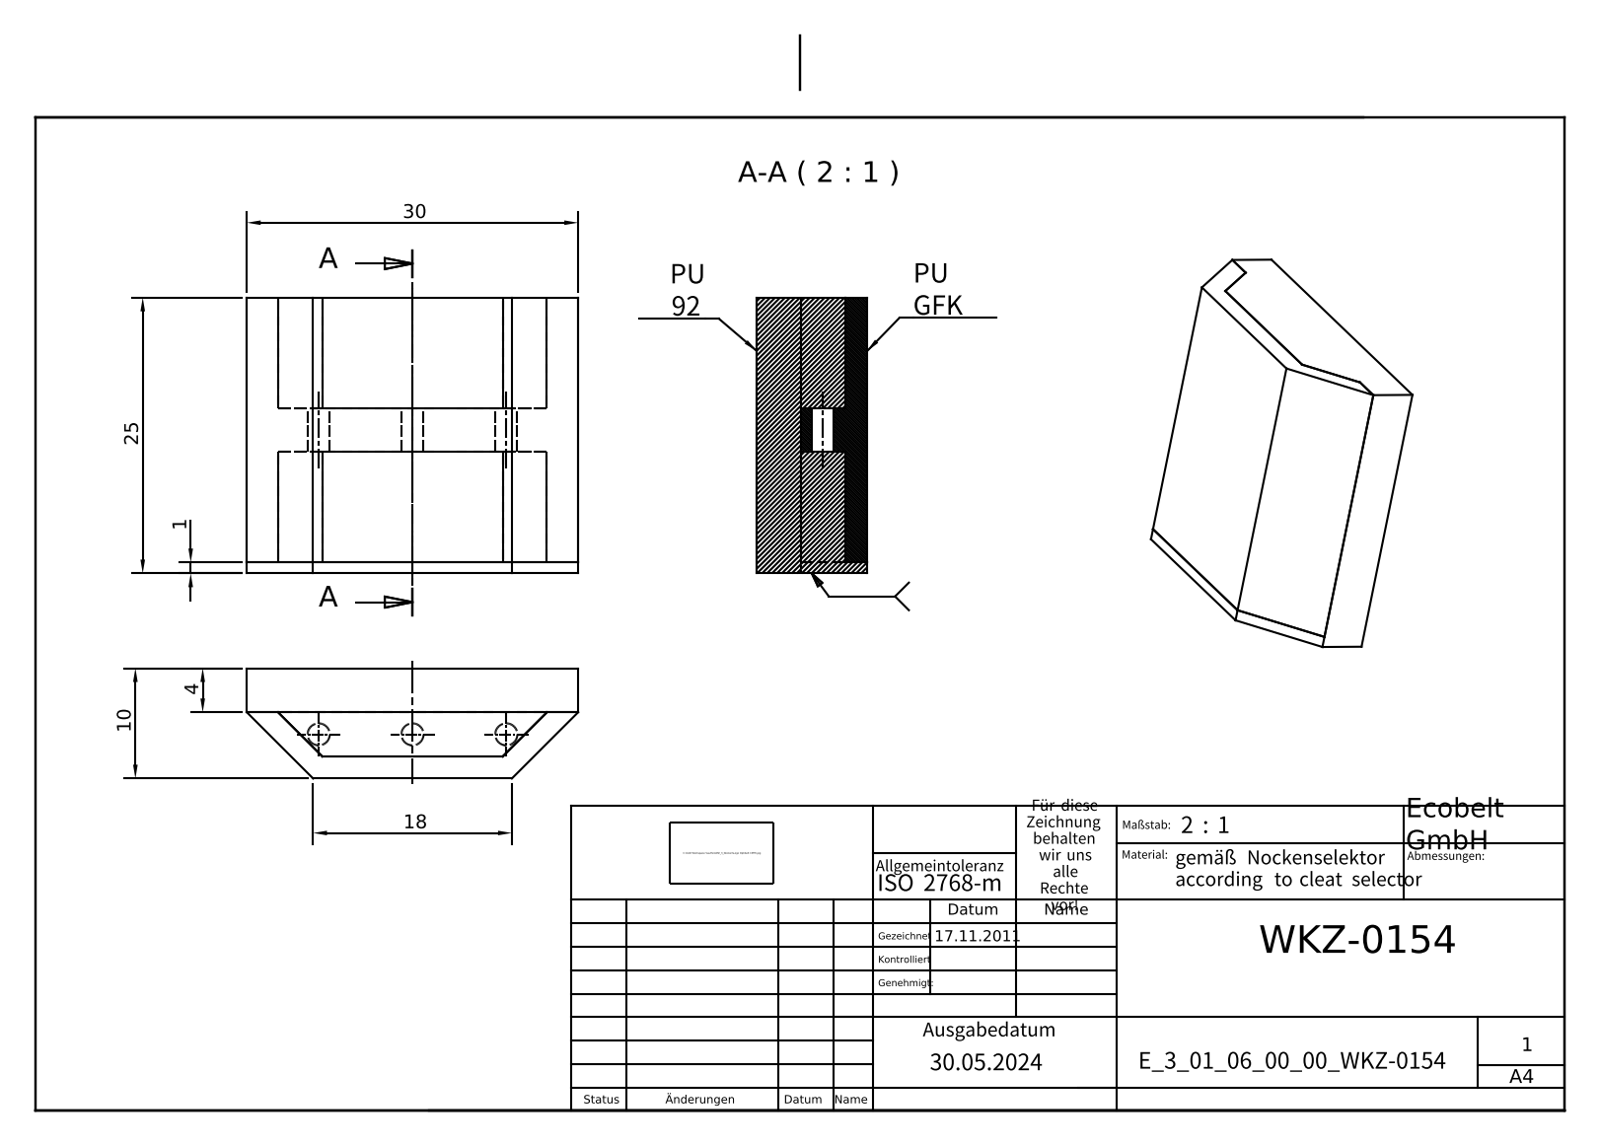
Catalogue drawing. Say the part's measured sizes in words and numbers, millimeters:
The part is named "E_3_01_06_00_00_WKZ-0154; E_3_01_06_00_00_WKZ-0154-Teil2; E_3_01_06_00_00_WKZ-0154-Teil1". Its 3-D file was written by "Autodesk Inventor 2025 (AUTOMOTIVE_DESIGN)". It is 2 solids with 35 faces: 32 planar, 3 cylindrical and 0 other. Overall it measures 30.01 by 25 by 10 millimeters. Its volume is 6 565 cubic millimeters and its surface area 4 434 square millimeters. Round holes: 3 of diameter 2. The main face-to-face distances are 4, 2, 10, 8, 6, 14, 25, 11, 15, 1. The hole center spacings are 8.5, 17.
